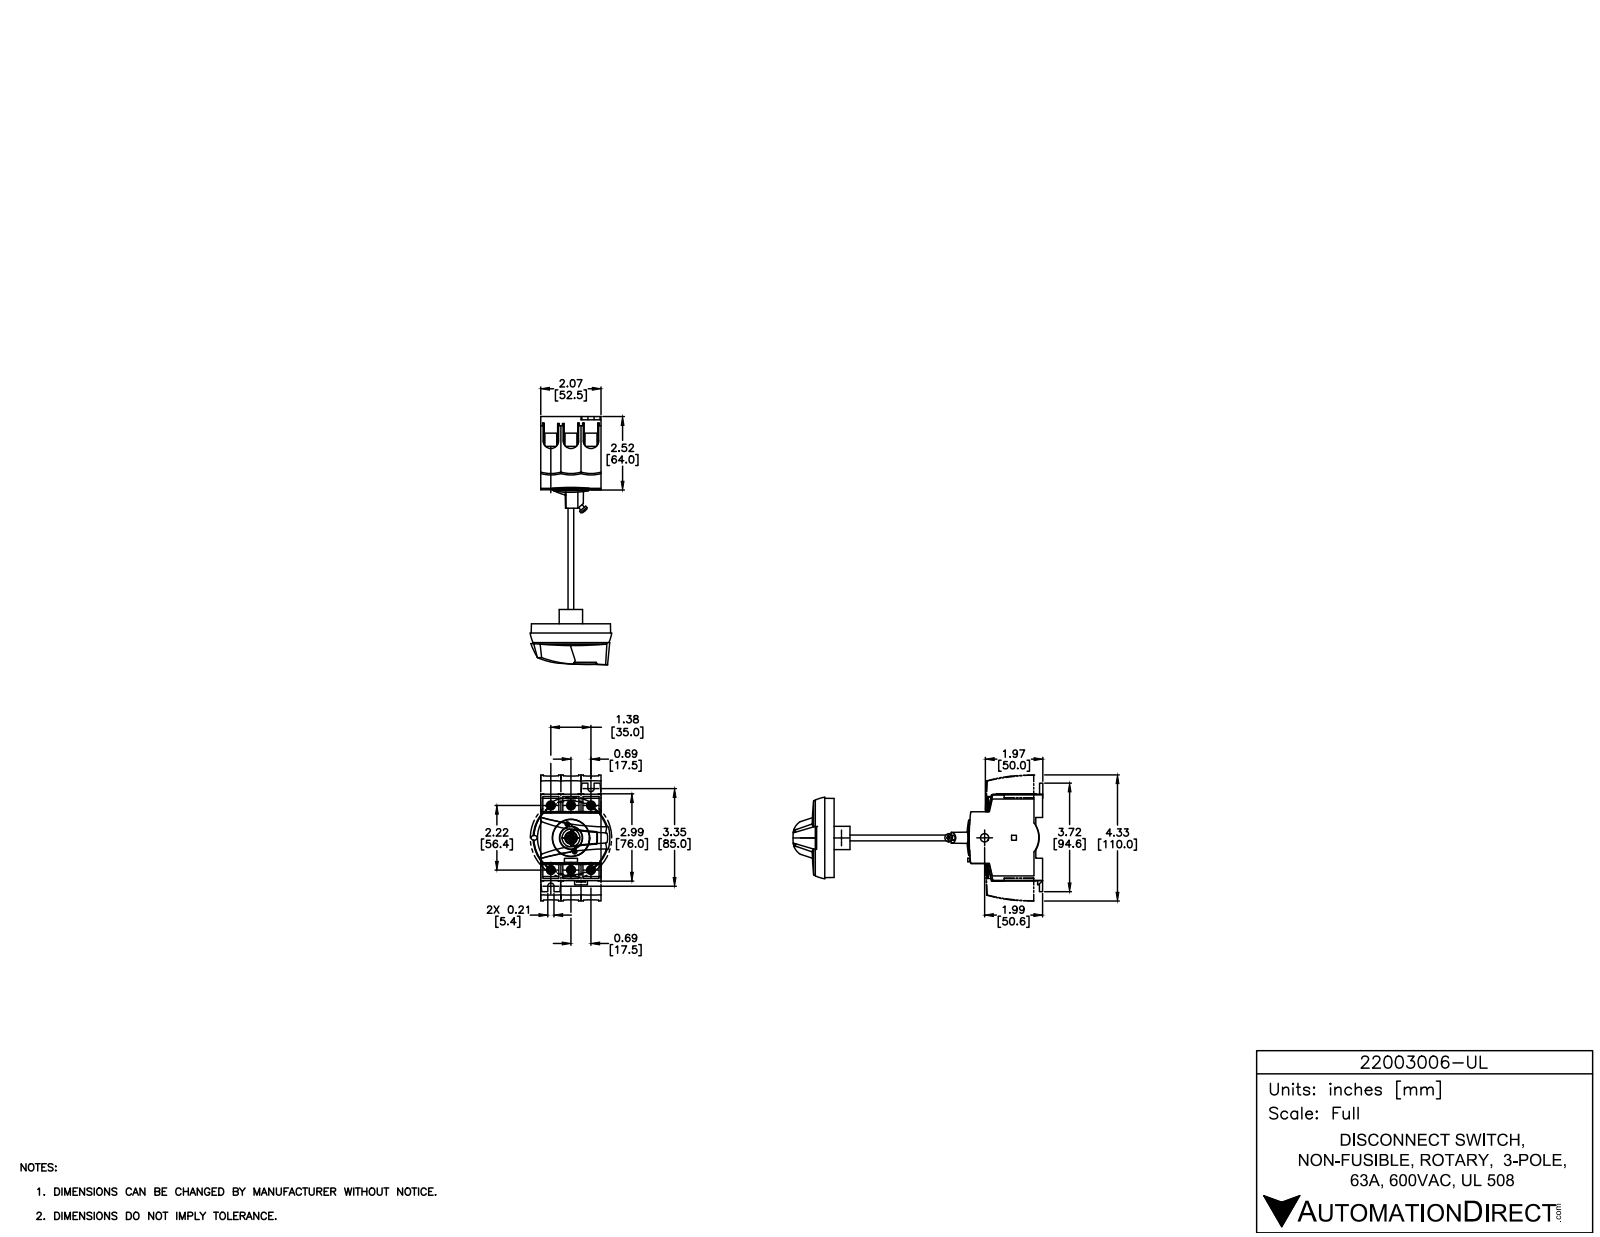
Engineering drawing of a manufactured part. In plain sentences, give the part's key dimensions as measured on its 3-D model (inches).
The part is named "22003006-UL". Its 3-D file was written by "SolidWorks 2015 (AUTOMOTIVE_DESIGN)". It is 1 solid with 238 faces: 199 planar, 39 cylindrical and 0 other. Overall it measures 3.724 by 2.576 by 2.067 inches. Its volume is 12.81 cubic inches and its surface area 42.15 square inches. Round holes: 6 of diameter 0.26, 1 of diameter 0.283, 1 of diameter 1.26. Partial cylindrical surfaces (rounded edges, fillets, slot ends): 9 of radius 1.18, 4 of radius 0.012, 2 of radius 0.106, 1 of radius 0.37, 1 of radius 0.827, 1 of radius 7.862. The main face-to-face distances are 2.067, 2.969, 2.391, 2.382, 0.61, 0.142, 2.827, 0.587, 2.358, 1.772. The hole center spacings are 0.689, 1.307, 2.325, 2.22, 1.11, 1.378, 2.613.
